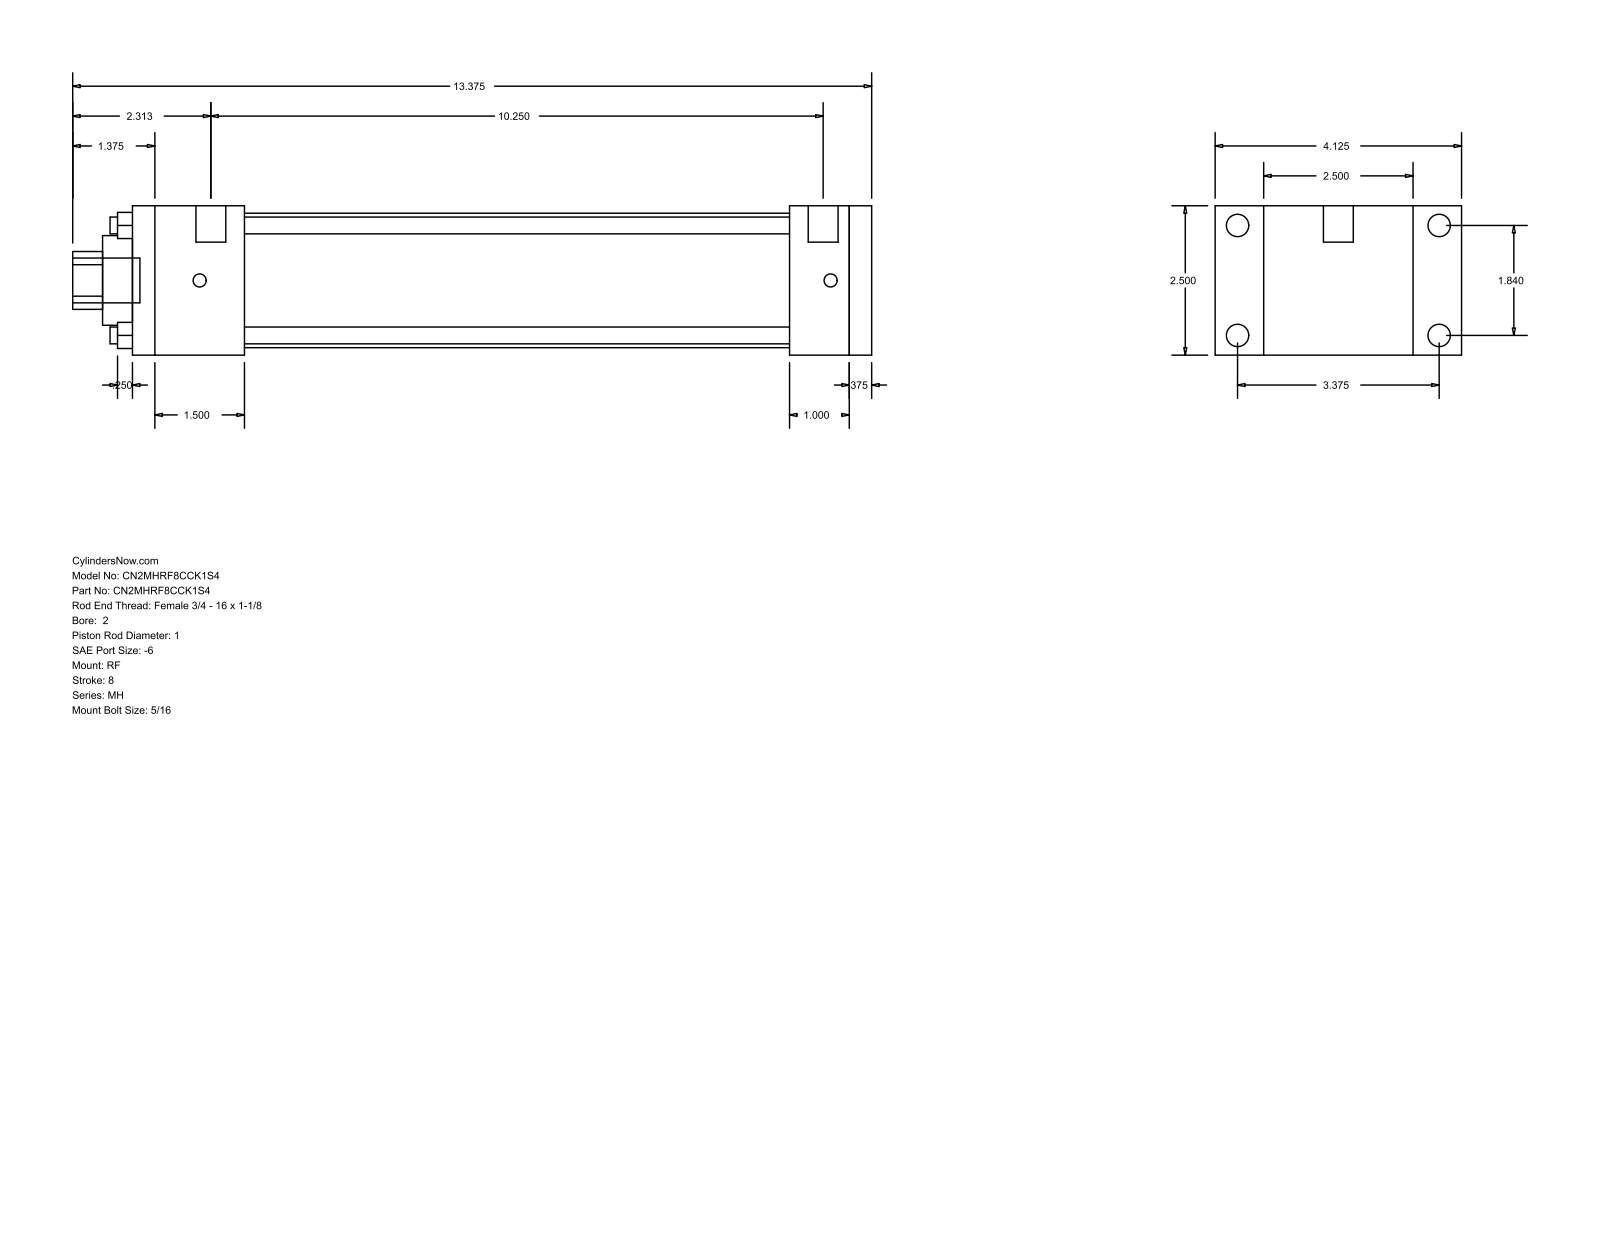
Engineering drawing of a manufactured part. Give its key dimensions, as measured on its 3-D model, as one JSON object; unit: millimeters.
{"part_name": "MH_RF__0200_1", "step_written_by": "GSSL Pune (CONFIG_CONTROL_DESIGN)", "units": "millimeters", "bodies": {"solids": 0, "faces": 92, "planar": 64, "cylindrical": 28, "other": 0}, "overall_size": [339.73, 104.78, 63.5], "round_holes": [[7.14, 4], [25.4, 1], [38.1, 1], [57.15, 1]], "round_bosses_or_shafts": [[9.53, 4], [5.56, 4], [12.7, 2], [19.05, 1]], "partial_cylinders_radius": [[12.29, 1]], "face_to_face_distances": [63.5, 314.33, 304.8, 9.53, 20.64, 25.4, 47.63, 279.4, 231.77, 257.17], "hole_center_spacings": [33.05, 46.74, 66.1]}
